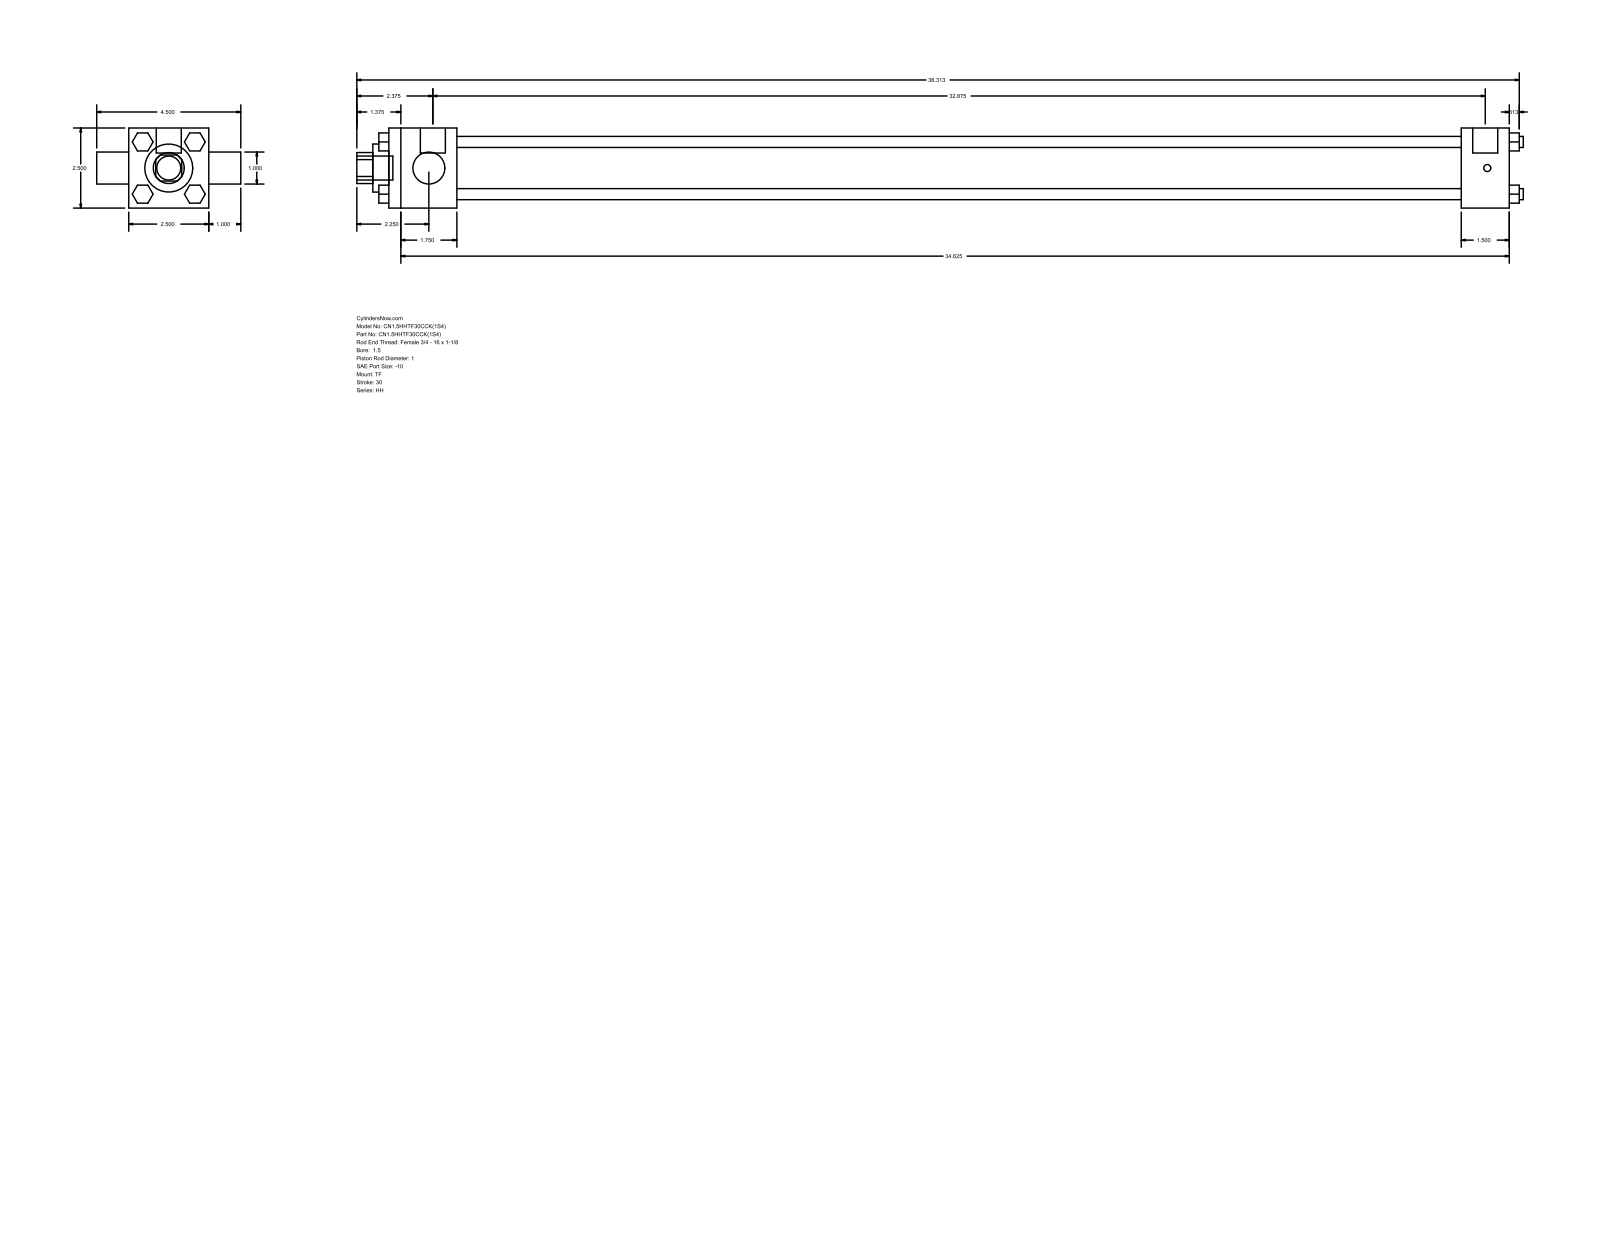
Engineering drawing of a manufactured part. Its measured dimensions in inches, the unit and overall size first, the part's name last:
Units: inches
Overall size (bounding box): 36.437 × 4.5 × 2.5
Round holes (diameter × count): ⌀1 ×2, ⌀1.5 ×1, ⌀1.75 ×1
Round bosses / shafts (diameter × count): ⌀0.345 ×4, ⌀0.219 ×3, ⌀0.781 ×2, ⌀0.75 ×1
Partial cylindrical surfaces — rounded edges, fillets, slot ends (radius × count): R0.484 ×1
Main face-to-face distances: 2.5, 32.875, 31.375, 1.5, 2.125, 33.5, 35, 35.313, 1, 0.815
Bodies: 0 solids, 120 faces (92 planar, 28 cylindrical, 0 other)
Part name (STEP PRODUCT): HH_TF__0150_1
STEP written by: GSSL Pune (CONFIG_CONTROL_DESIGN)
